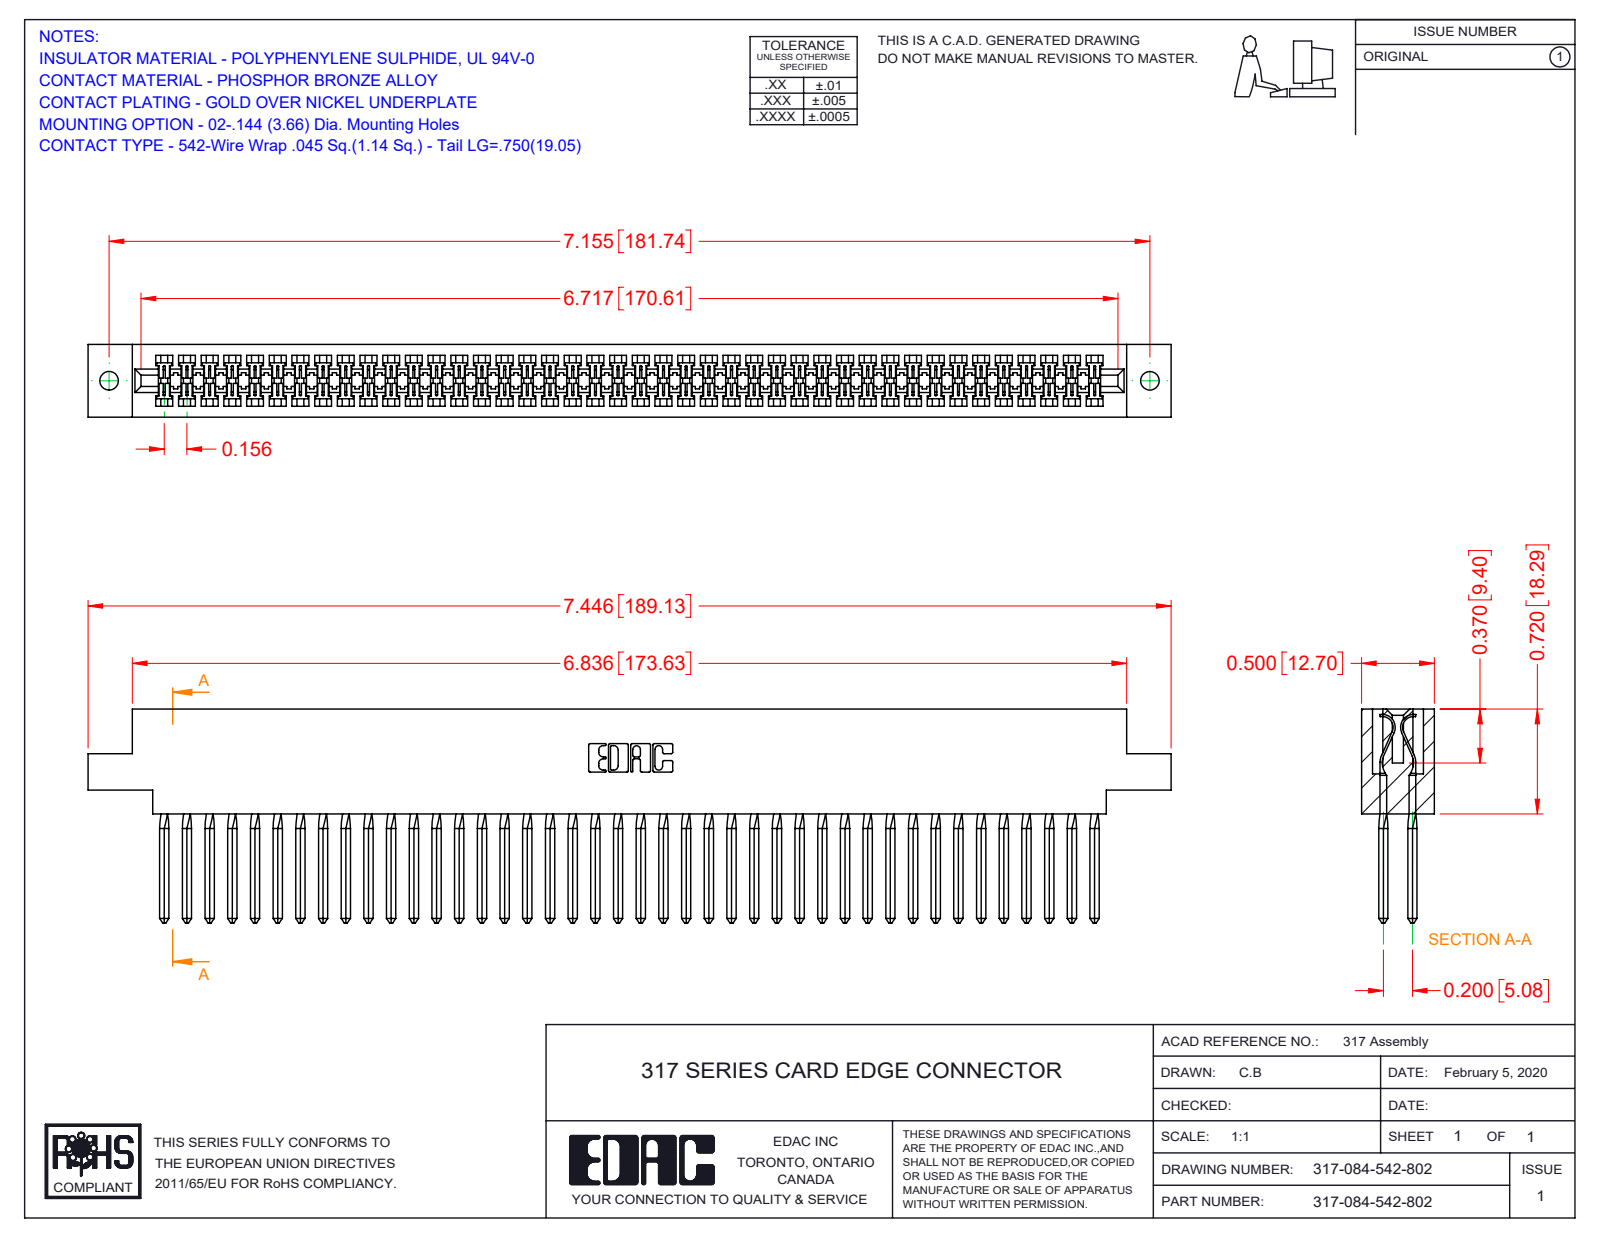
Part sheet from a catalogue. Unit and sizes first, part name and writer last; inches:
Units: inches
Overall size (bounding box): 7.446 × 1.47 × 0.5
Round holes (diameter × count): ⌀0.128 ×2
Partial cylindrical surfaces — rounded edges, fillets, slot ends (radius × count): R0.006 ×168, R0.01 ×22, R0.007 ×6, R0.031 ×6, R0.026 ×3, R0.074 ×2, R0.089 ×2, R0.1 ×2
Main face-to-face distances: 0.5, 0.075, 0.425, 0.35, 0.2, 0.046, 0.128, 0.372, 0.052, 0.297
Hole centre spacings: 7.155
Volume: 1.888 in³ · Surface area: 66.26 in²
Bodies: 85 solids, 4890 faces (3922 planar, 632 cylindrical, 336 other)
Part name (STEP PRODUCT): 317-084-542-802; 317-290-003_542; 317 Part_.144 Dia
STEP written by: SolidWorks 2016 (CONFIG_CONTROL_DESIGN)
